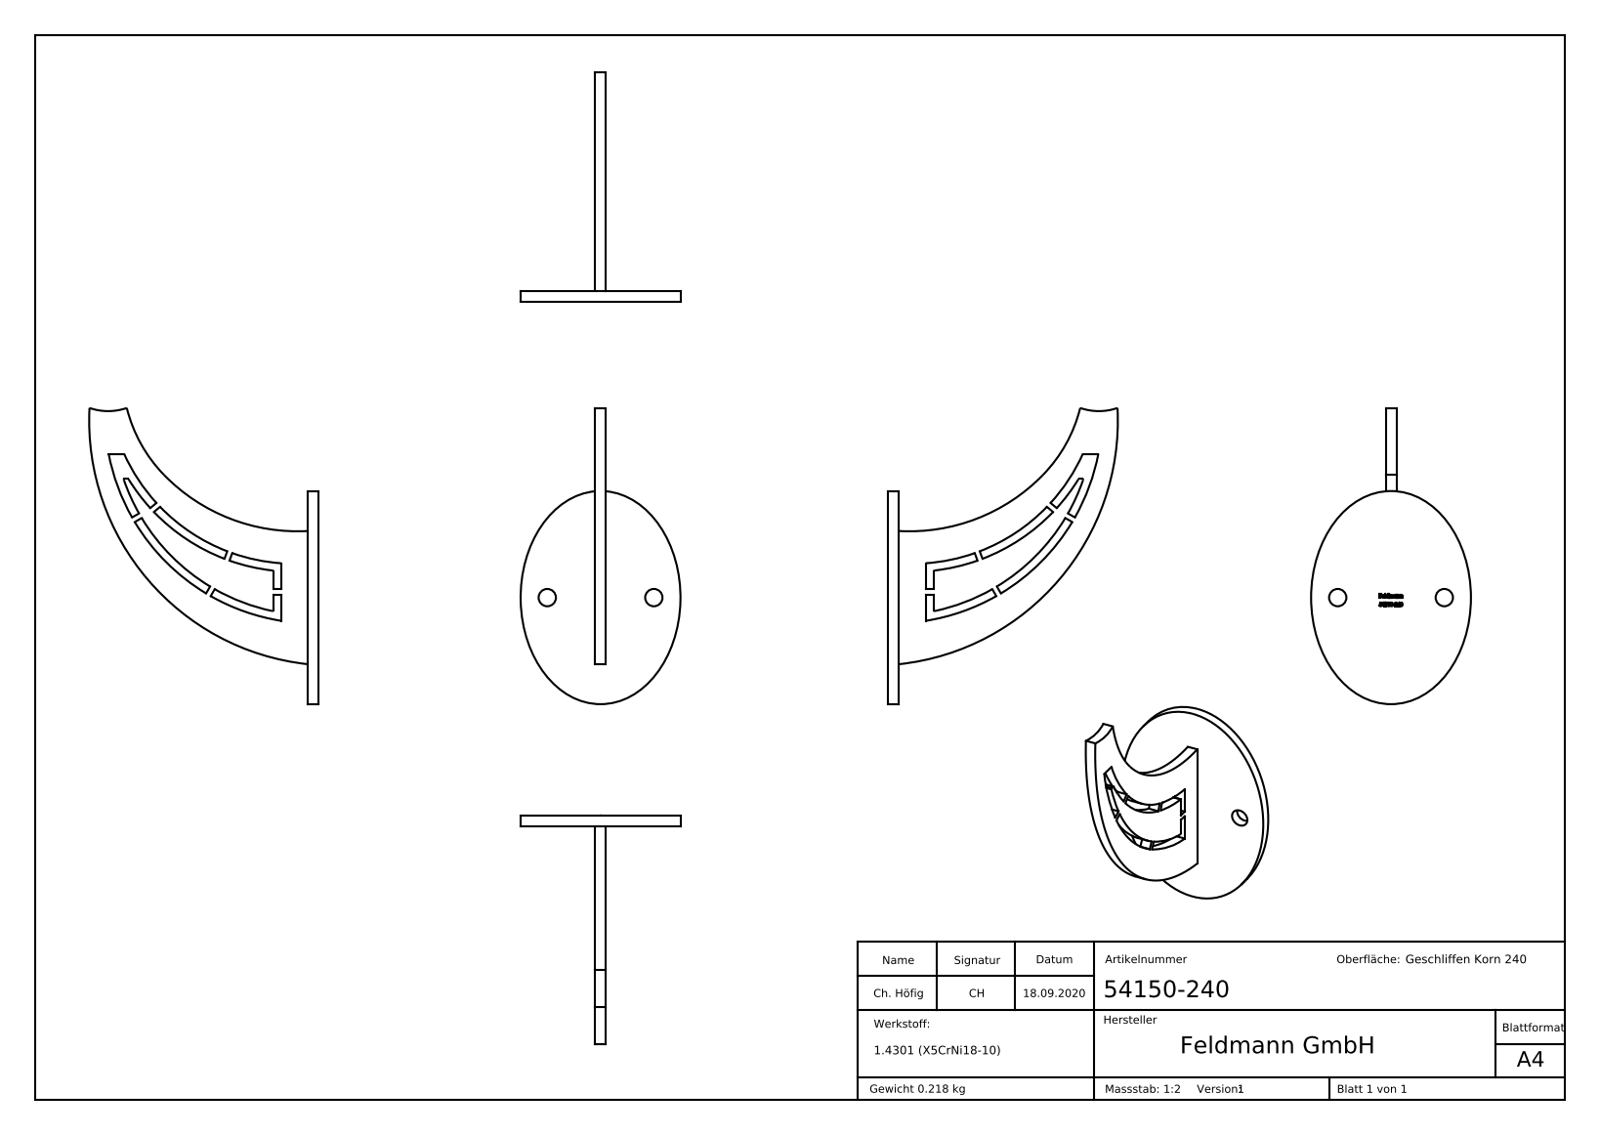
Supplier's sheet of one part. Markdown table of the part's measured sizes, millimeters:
| quantity | value |
| --- | --- |
| part name | 54150-240 |
| STEP written by | SolidWorks 2018 (CONFIG_CONTROL_DESIGN) |
| units | millimeters |
| bodies | 1 solid, 266 faces (152 planar, 24 cylindrical, 90 other) |
| overall size | 111.19 × 86.12 × 60 |
| volume | 27 599 mm³ |
| surface area | 17 108 mm² |
| round holes (diameter × count) | 6.5 × 2 |
| partial cylindrical surfaces (radius × count) | 0.25 × 4, 70 × 2, 21.2 × 1, 55 × 1, 73 × 1, 75.5 × 1, 78.5 × 1, 92 × 1 |
| main face-to-face distances | 4, 14.1, 10.1, 2, 17.1, 13.1, 3, 52.9, 50.9, 3.9 |
| hole center spacings | 40 |
